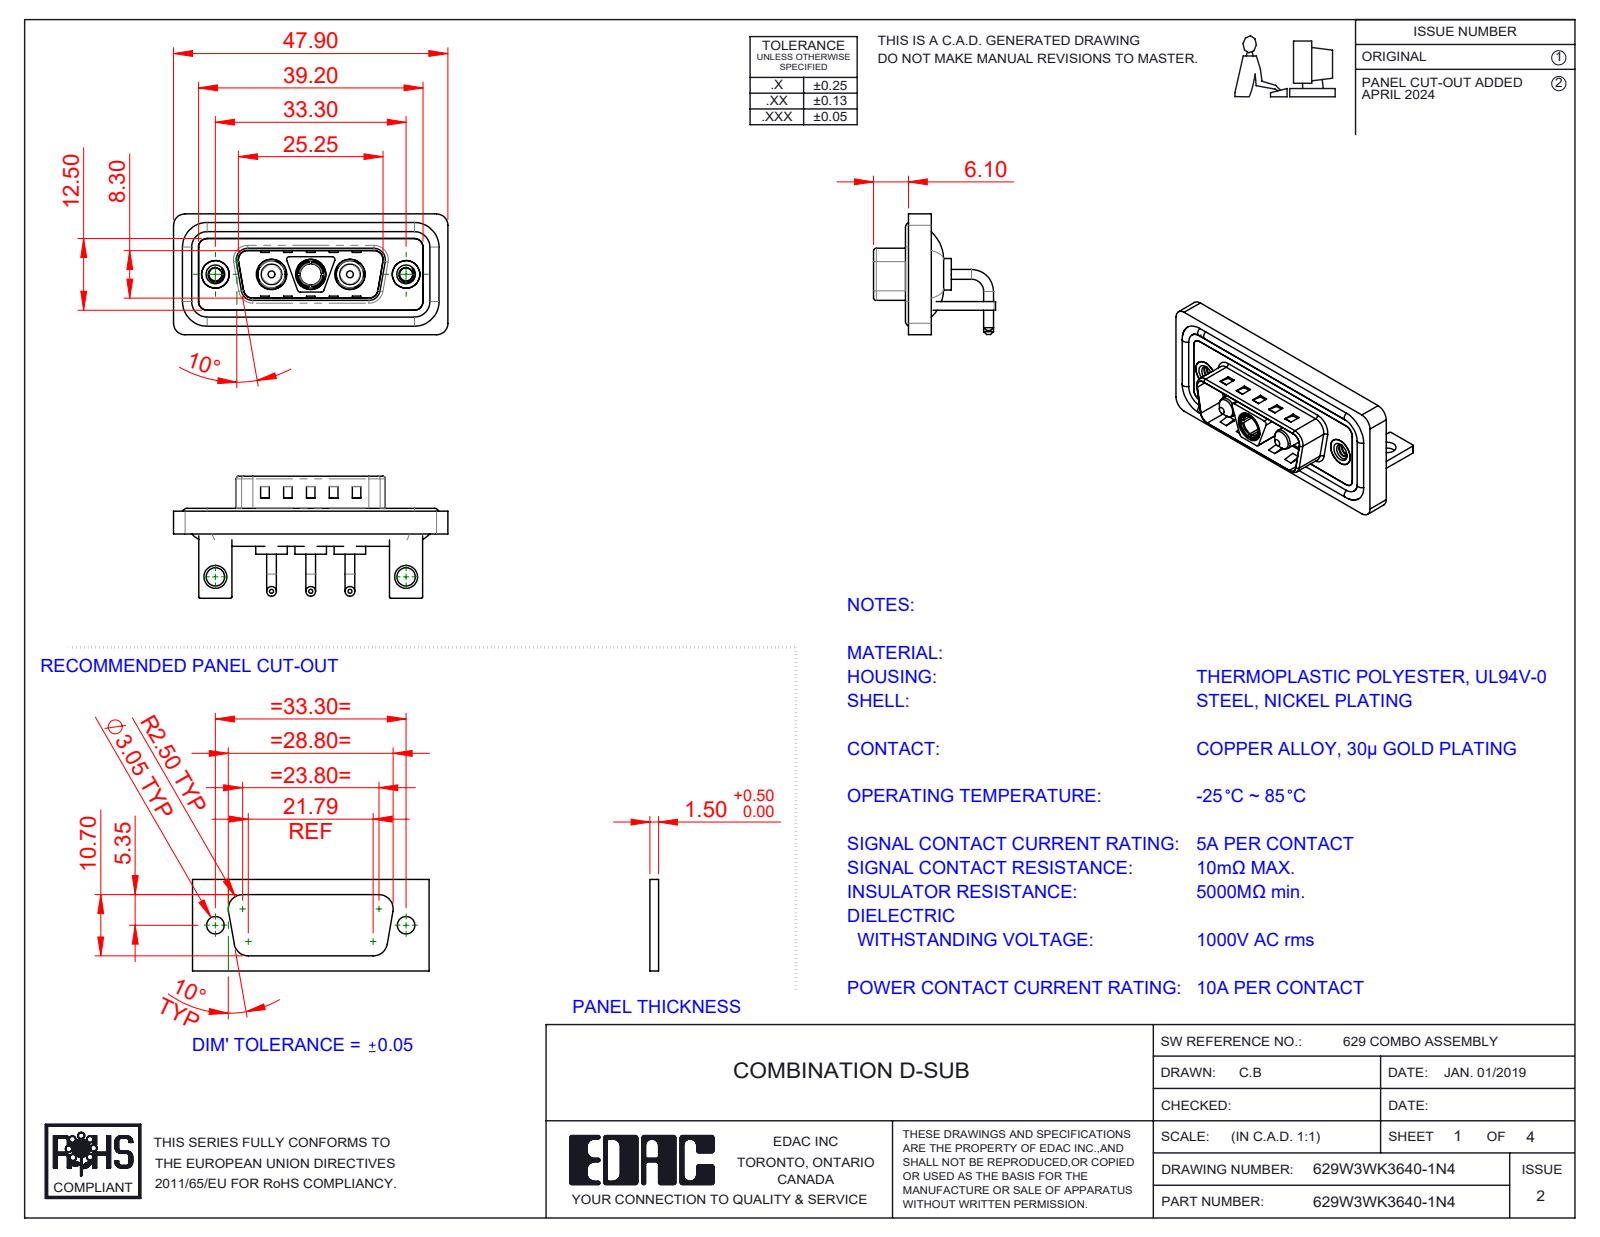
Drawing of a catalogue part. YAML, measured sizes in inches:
part_name: "629Combo Waterproof Housing_15 Contacts; Power Socket_10A RA; 629W3WK3640-1N4; 629Combo Housing_3WK3 (+5 more)"
step_written_by: "SolidWorks 2023 (CONFIG_CONTROL_DESIGN)"
units: inches
bodies: {solids: 15, faces: 661, planar: 251, cylindrical: 274, other: 136}
overall_size: [1.886, 0.839, 0.831]
volume: 0.365
surface_area: 15.26
round_holes:
  - {diameter: 0.191, count: 3}
  - {diameter: 0.209, count: 3}
  - {diameter: 0.089, count: 2}
  - {diameter: 0.126, count: 2}
  - {diameter: 0.157, count: 2}
  - {diameter: 0.189, count: 2}
  - {diameter: 0.197, count: 2}
  - {diameter: 0.146, count: 1}
round_bosses_or_shafts:
  - {diameter: 0.067, count: 6}
  - {diameter: 0.063, count: 4}
  - {diameter: 0.217, count: 3}
  - {diameter: 0.205, count: 3}
  - {diameter: 0.187, count: 3}
  - {diameter: 0.148, count: 3}
  - {diameter: 0.193, count: 2}
  - {diameter: 0.142, count: 2}
partial_cylinders:
  - {radius: 0.079, count: 21}
  - {radius: 0.059, count: 18}
  - {radius: 0.01, count: 16}
  - {radius: 0.02, count: 13}
  - {radius: 0.063, count: 8}
  - {radius: 0.024, count: 4}
  - {radius: 0.026, count: 4}
  - {radius: 0.035, count: 4}
face_to_face_distances: [0.016, 0.059, 0.031, 0.114, 0.043, 0.083, 0.146, 0.063, 0.047, 0.177]
hole_center_spacings: [0.27, 0.386, 0.656, 0.925, 1.311, 0.539]
